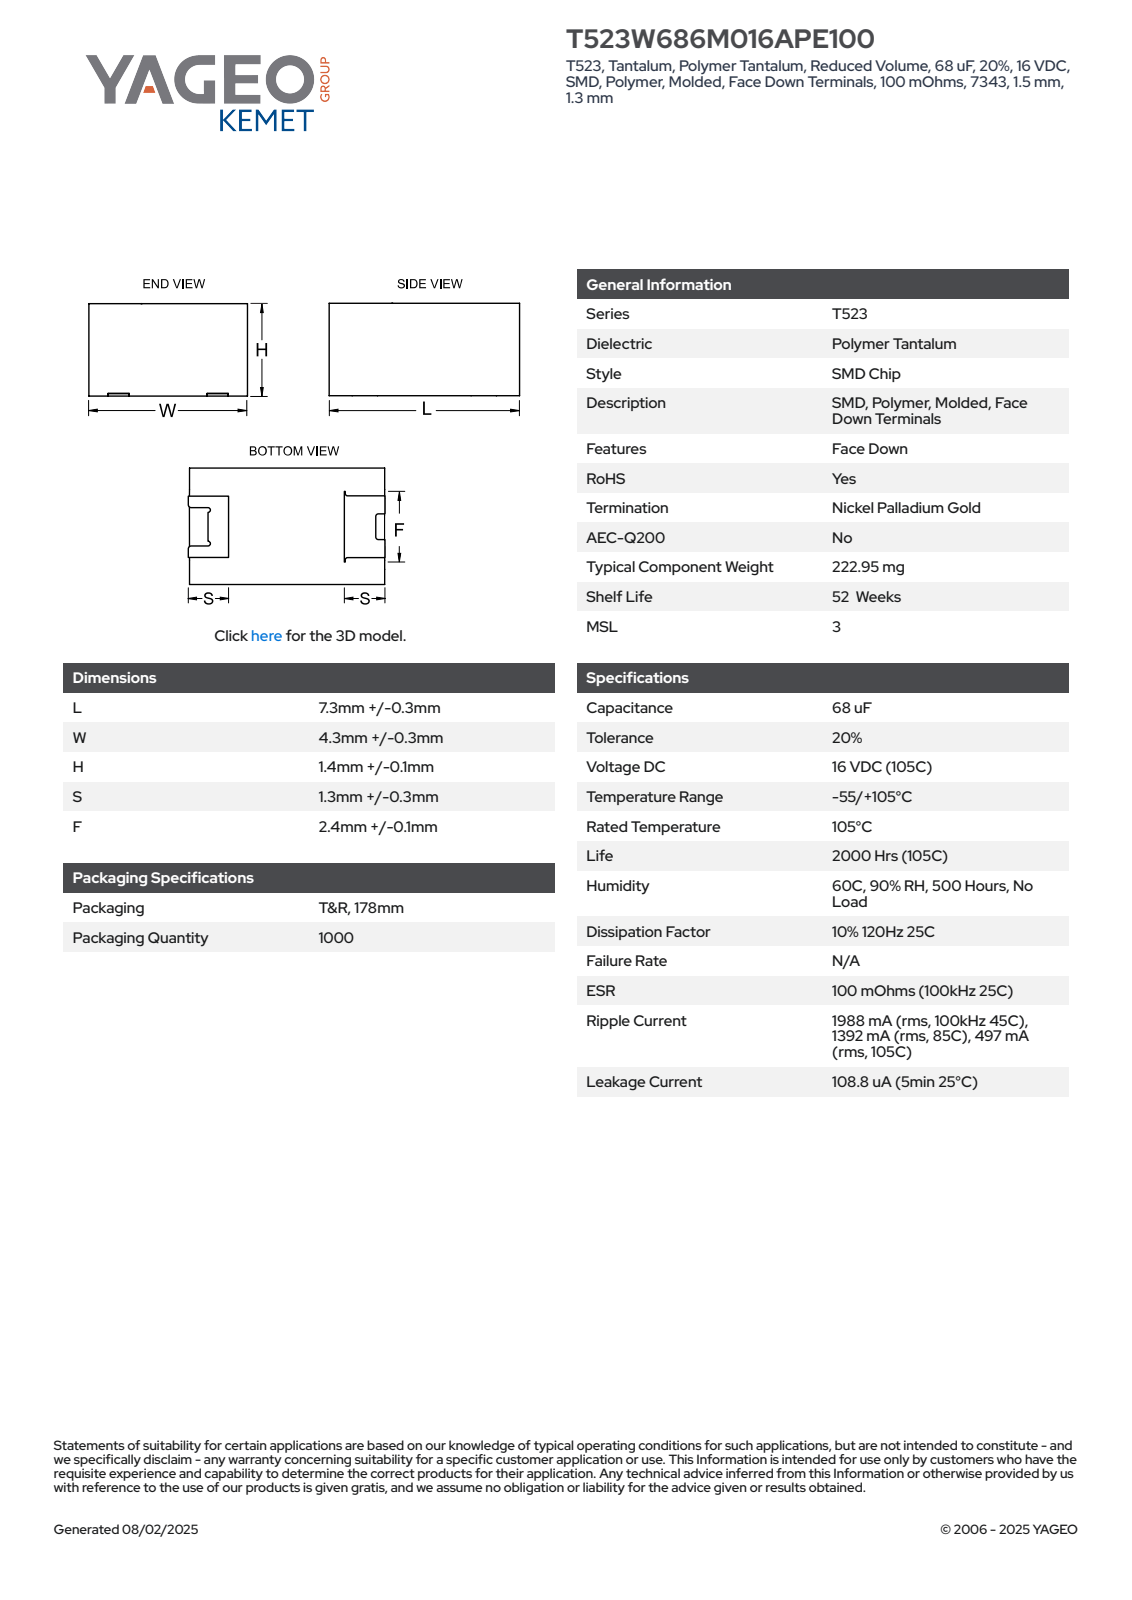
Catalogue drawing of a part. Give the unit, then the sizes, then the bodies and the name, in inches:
Units: inches
Overall size (bounding box): 0.3 × 0.181 × 0.059
Partial cylindrical surfaces — rounded edges, fillets, slot ends (radius × count): R0.006 ×2
Main face-to-face distances: 0.059, 0.181, 0.059, 0.299, 0.06, 0.3, 0.3, 0.039, 0.055, 0.066
Volume: 0.003 in³ · Surface area: 0.166 in²
Bodies: 1 solid, 88 faces (86 planar, 2 cylindrical, 0 other)
Part name (STEP PRODUCT): CTS_TFD_JVW_7343_L7.6W4.6H1.5S1.3F2.5
STEP written by: SolidWorks 2020 (AUTOMOTIVE_DESIGN)
